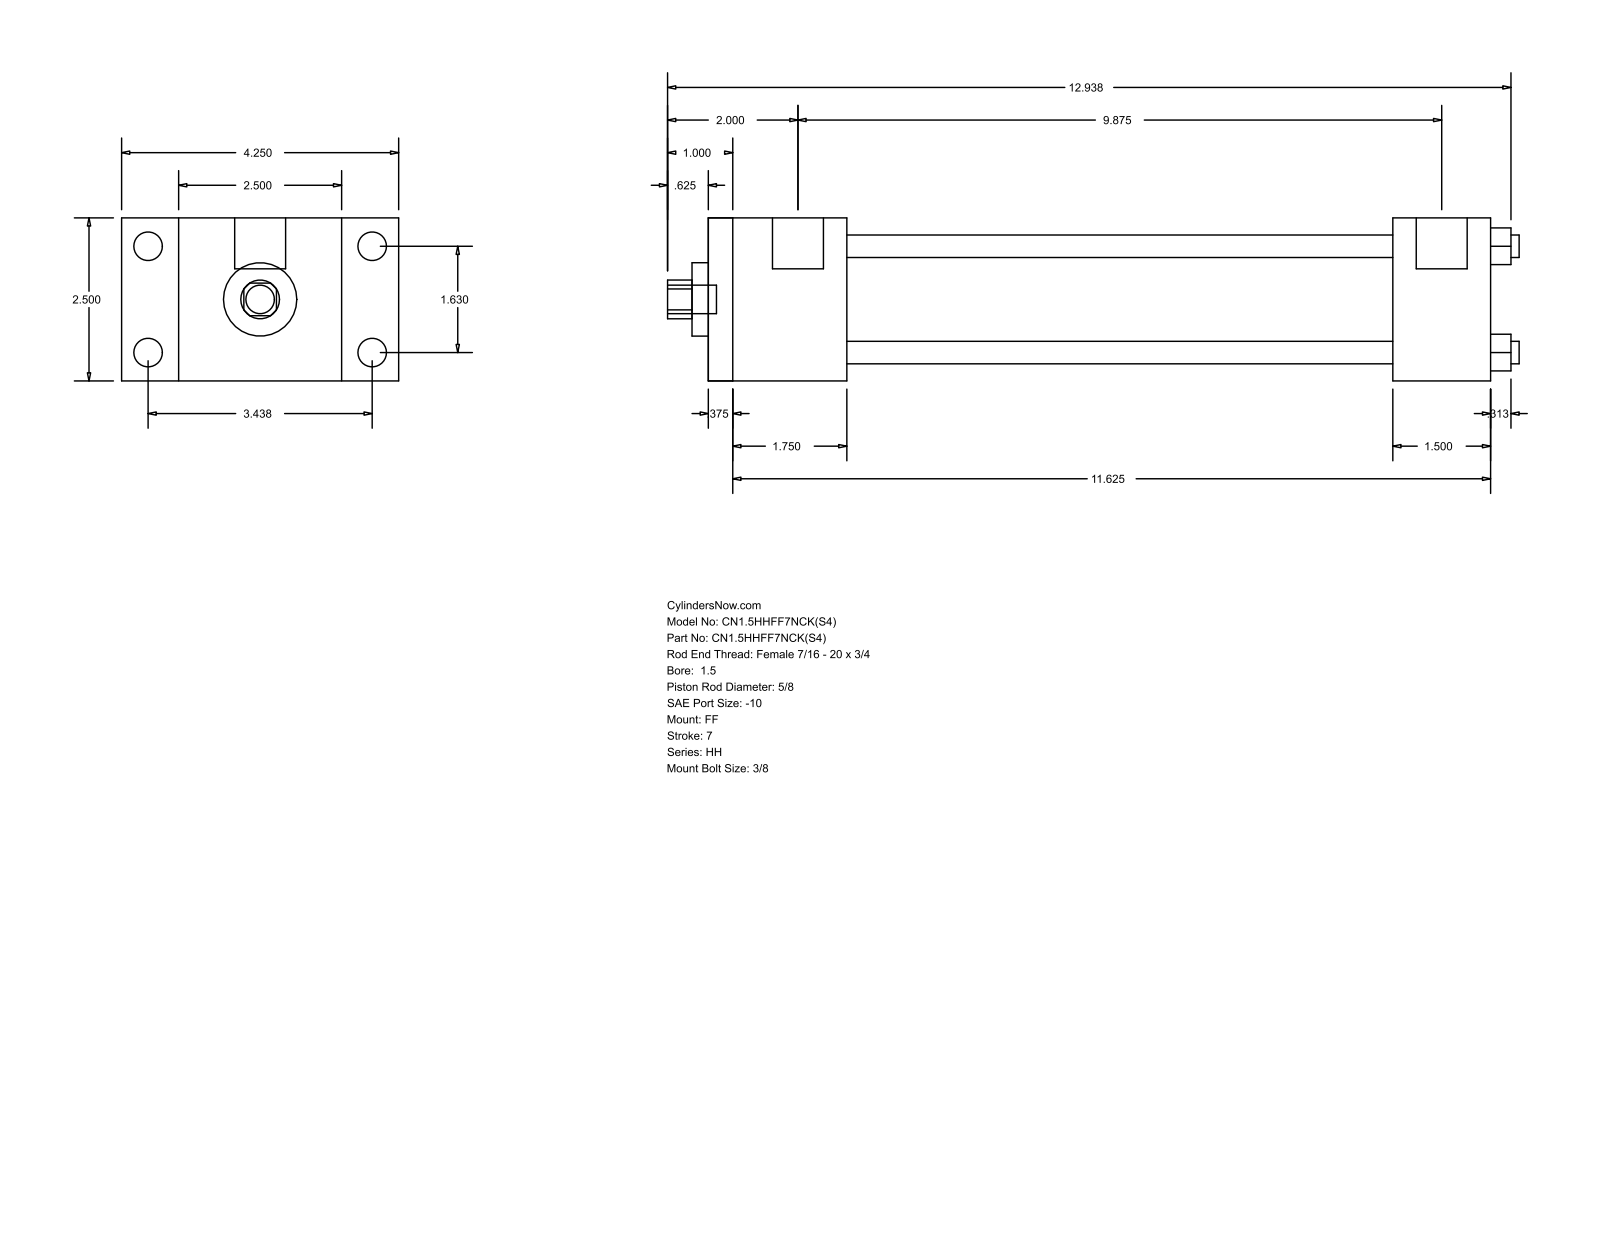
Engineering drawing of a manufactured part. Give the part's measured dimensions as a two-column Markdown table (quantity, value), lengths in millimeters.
| quantity | value |
| --- | --- |
| part name | HH_FF__0150_0.625 |
| STEP written by | GSSL Pune (CONFIG_CONTROL_DESIGN) |
| units | millimeters |
| bodies | 0 solids, 92 faces (64 planar, 28 cylindrical, 0 other) |
| overall size | 331.79 × 107.95 × 63.5 |
| round holes (diameter × count) | 8.76 × 4, 15.88 × 1, 28.57 × 1, 44.45 × 1 |
| round bosses / shafts (diameter × count) | 11.13 × 4, 5.56 × 4, 19.84 × 2, 11.11 × 1 |
| partial cylindrical surfaces (radius × count) | 7.54 × 1 |
| main face-to-face distances | 63.5, 304.8, 9.52, 295.28, 53.97, 44.45, 250.83, 266.69, 257.17, 212.72 |
| hole center spacings | 29.27, 41.4, 58.55 |
